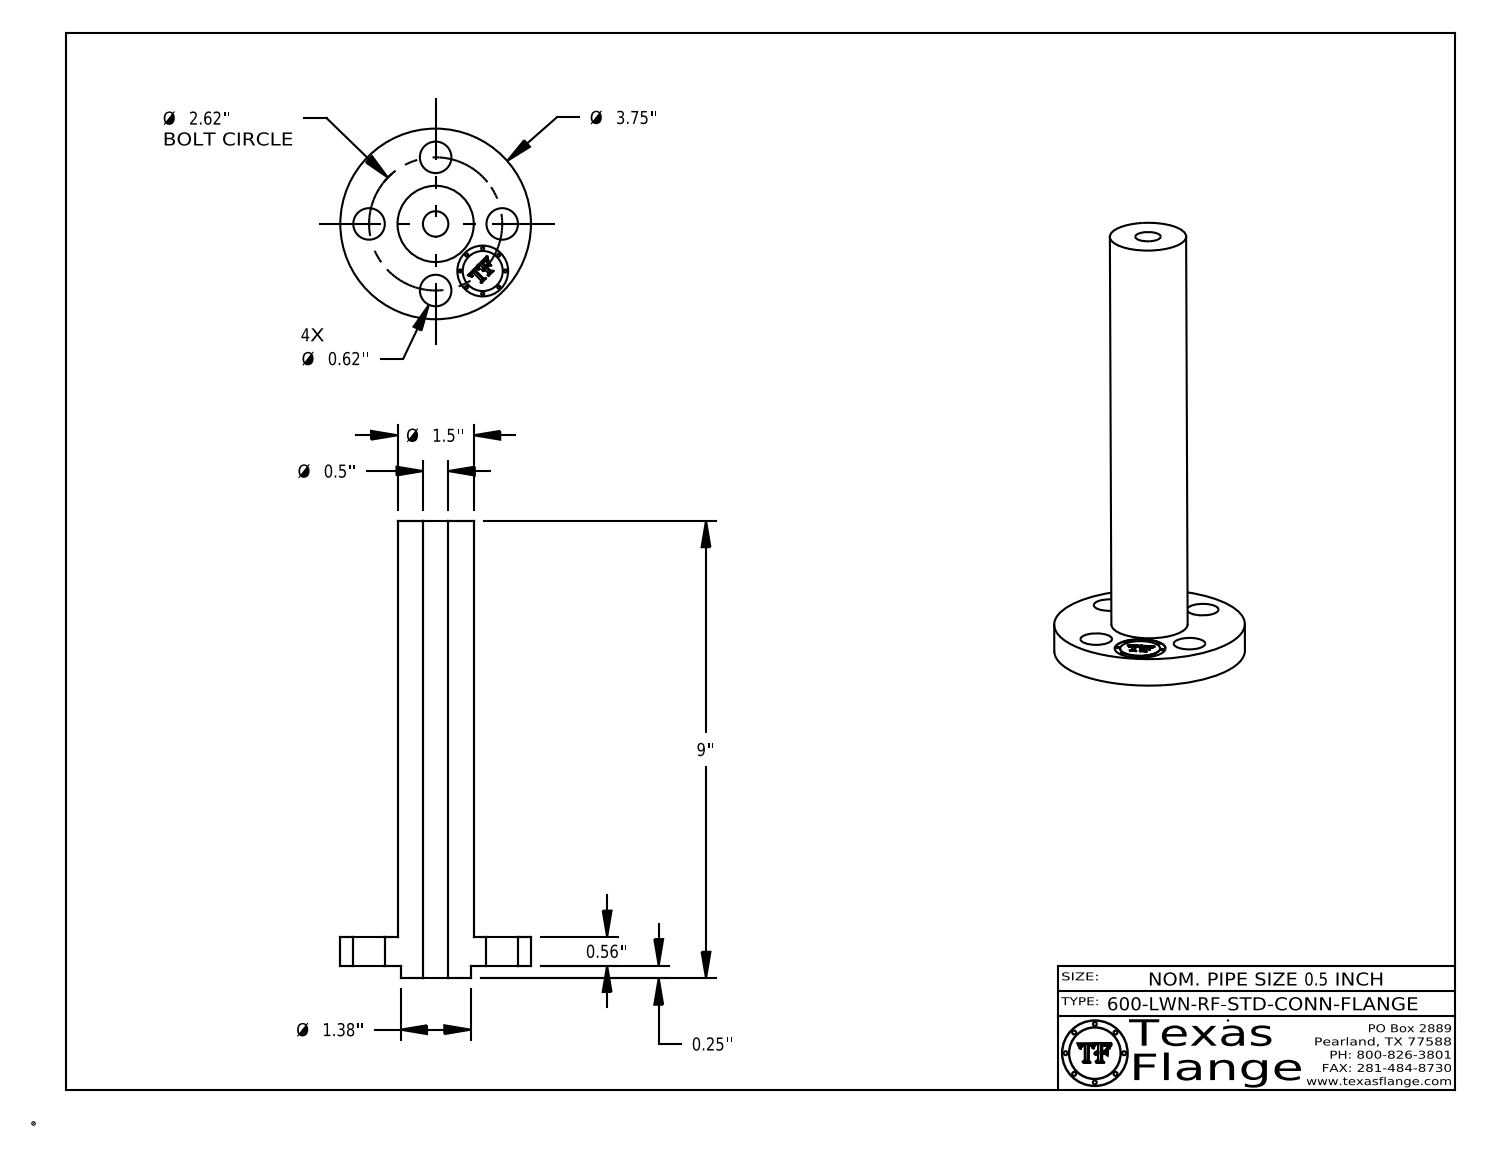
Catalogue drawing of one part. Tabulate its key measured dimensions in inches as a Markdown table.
| quantity | value |
| --- | --- |
| part name | 0.5-600-LWN-RF-STD-CONN-FLANGE |
| STEP written by | CATIA V5 STEP AP214 (AUTOMOTIVE_DESIGN) |
| units | inches |
| bodies | 1 solid, 405 faces (369 planar, 36 cylindrical, 0 other) |
| overall size | 9 × 3.75 × 3.75 |
| volume | 18.59 in³ |
| surface area | 84.12 in² |
| round holes (diameter × count) | 0.62 × 4, 0.5 × 1, 1 × 1 |
| round bosses / shafts (diameter × count) | 0.061 × 8, 3.75 × 1, 1.5 × 1, 1.38 × 1, 0.788 × 1 |
| main face-to-face distances | 0.56, 8.75, 8.19, 0.25, 0.81, 9, 0.805, 0.555, 8.195, 0.298 |
| hole center spacings | 1.31, 1.852, 1.003, 2.42, 2.62, 1.31 |
